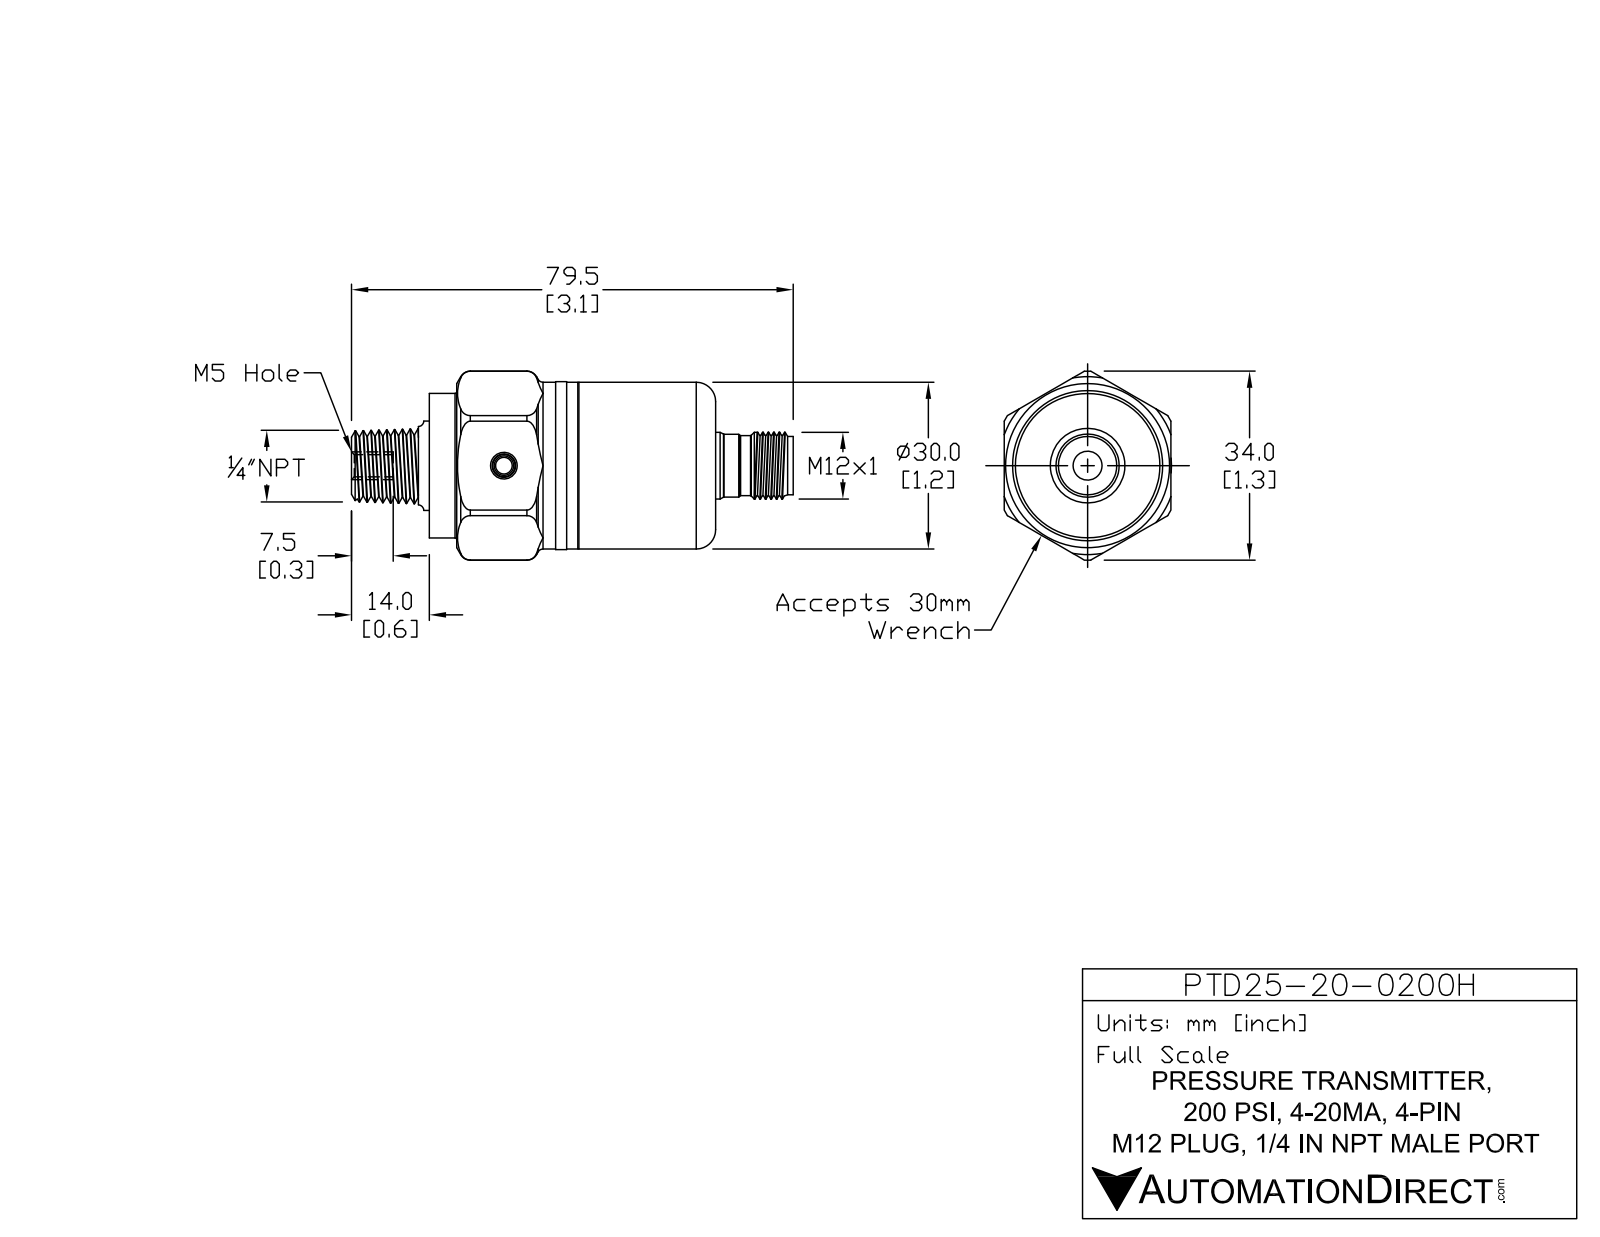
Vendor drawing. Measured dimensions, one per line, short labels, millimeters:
name: PTD25-20-0200H
written by: SolidWorks 2017 (AUTOMOTIVE_DESIGN)
unit: mm
bodies: 1 solid, 124 faces (36 planar, 59 cylindrical, 29 other)
size: 79.5 × 33.78 × 31.7
volume: 39 212 mm³; area: 8 088 mm²
holes: 1× ⌀4, 1× ⌀8.5
bosses: 1× ⌀30.05, 1× ⌀30, 1× ⌀25.96, 1× ⌀14, 1× ⌀13.5, 1× ⌀12
rounds: 1× R3.76, 1× R16.95
face distances: 51, 29.98, 30, 48, 3, 65, 17, 14, 30.01, 5.65
